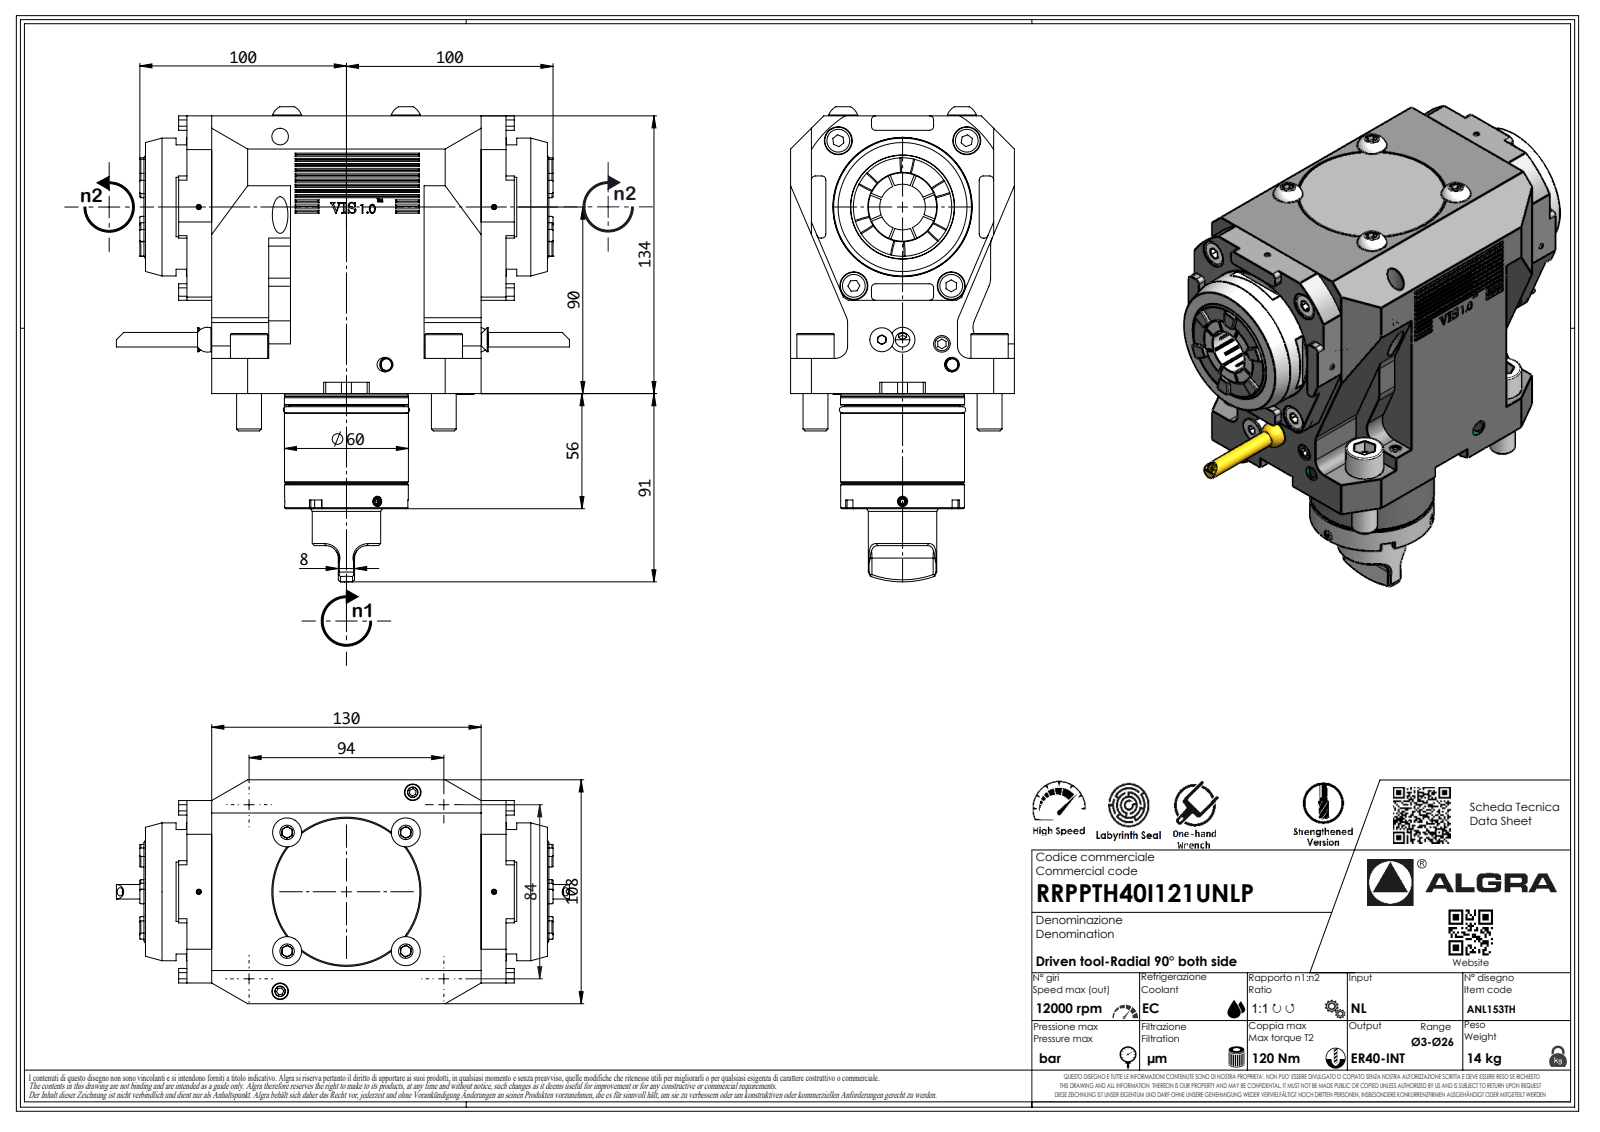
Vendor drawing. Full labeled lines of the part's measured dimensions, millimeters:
Part name (STEP PRODUCT): RRPPTH40I121UNLP
STEP written by: SolidWorks 2023 (AUTOMOTIVE_DESIGN)
Units: millimetres
Bodies: 1 solid, 1076 faces (708 planar, 176 cylindrical, 192 other)
Overall size (bounding box): 224.8 × 218.64 × 108
Volume: 2 140 000 mm³ · Surface area: 161 404 mm²
Round holes (diameter × count): ⌀6 ×4, ⌀7 ×3, ⌀4 ×2, ⌀2.1 ×1, ⌀55.2 ×1, ⌀59.2 ×1, ⌀63.2 ×1, ⌀67.2 ×1
Round bosses / shafts (diameter × count): ⌀18 ×4, ⌀12 ×4, ⌀67 ×1, ⌀66.5 ×1, ⌀63 ×1, ⌀59.9 ×1, ⌀59.8 ×1, ⌀59.7 ×1
Partial cylindrical surfaces — rounded edges, fillets, slot ends (radius × count): R0.2 ×21, R8 ×18, R2 ×16, R6 ×10, R0.33 ×7, R0.52 ×7, R3.7 ×7, R10 ×4
Main face-to-face distances: 108, 134, 12, 162, 32, 20, 174, 142, 39.5, 27.5
Hole centre spacings: 71.67, 77.77
